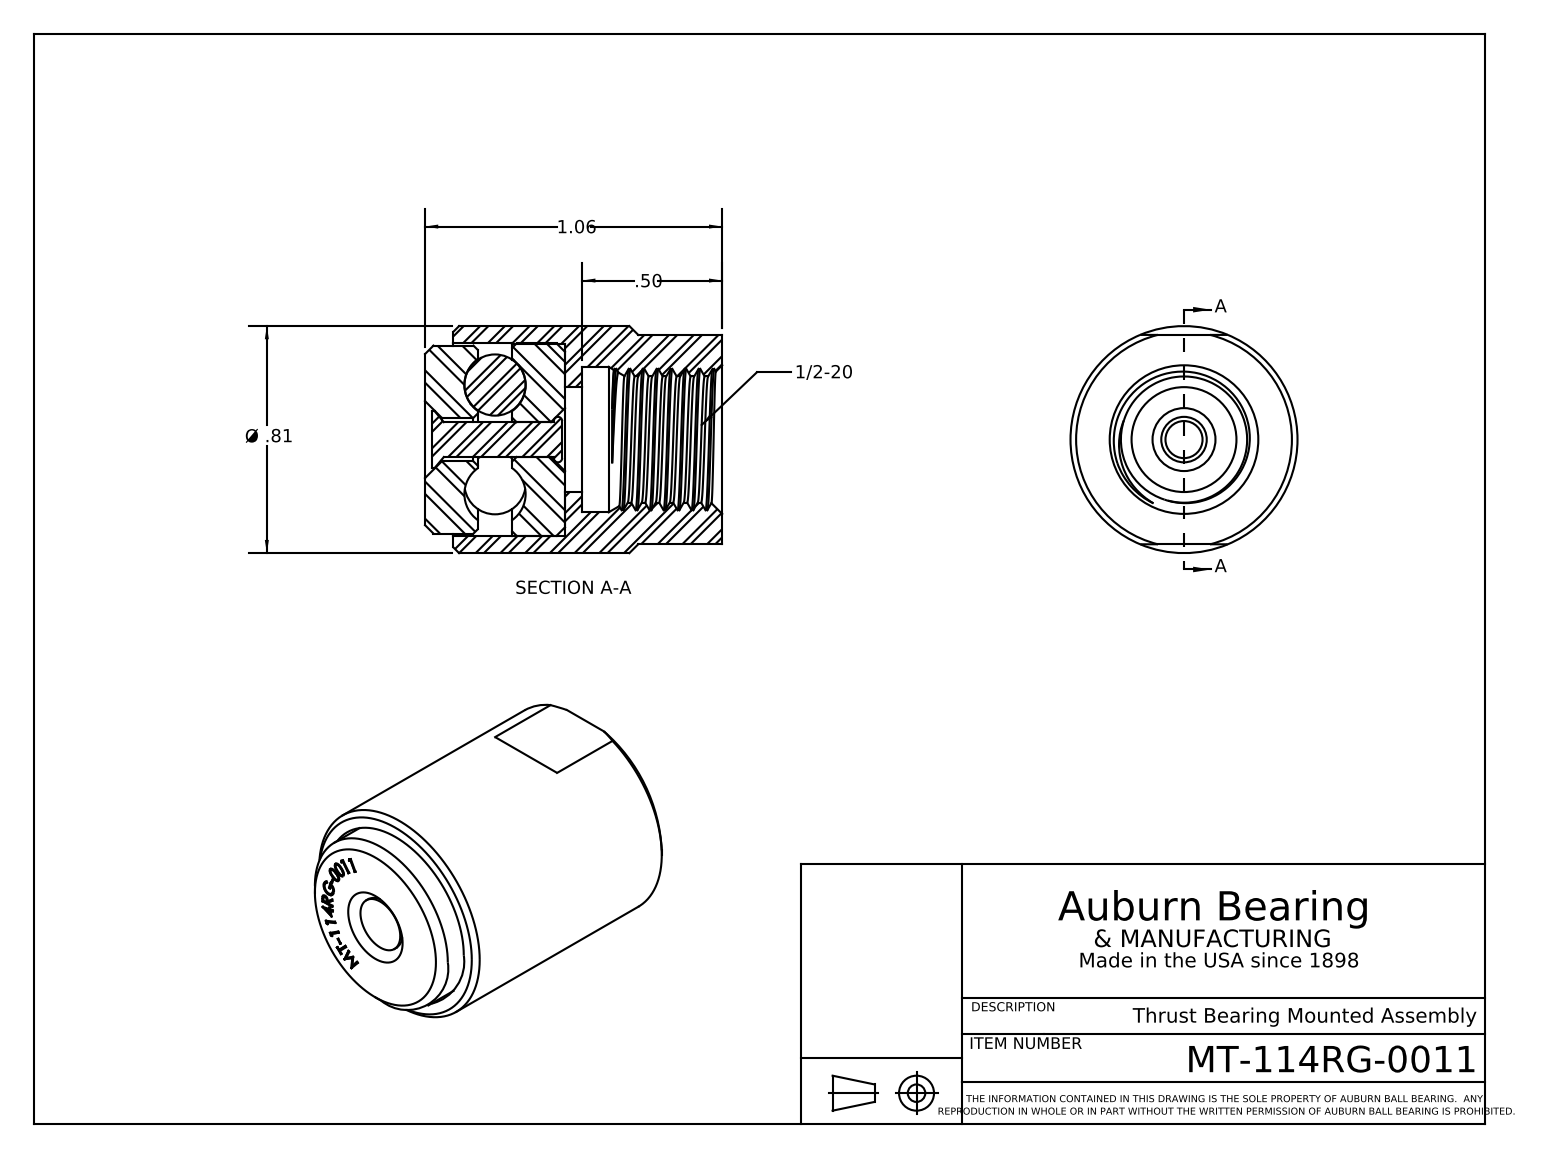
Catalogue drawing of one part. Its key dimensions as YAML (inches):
part_name: "MT-114RG-0011"
step_written_by: "SolidWorks 2020 (CONFIG_CONTROL_DESIGN)"
units: inches
bodies: {solids: 9, faces: 233, planar: 116, cylindrical: 36, other: 81}
overall_size: [1.062, 0.811, 0.811]
volume: 0.388
surface_area: 8.537
round_holes:
  - {diameter: 0.125, count: 1}
  - {diameter: 0.156, count: 1}
  - {diameter: 0.375, count: 1}
  - {diameter: 0.451, count: 1}
  - {diameter: 0.52, count: 1}
  - {diameter: 0.687, count: 1}
  - {diameter: 0.69, count: 1}
round_bosses_or_shafts:
  - {diameter: 0.811, count: 1}
  - {diameter: 0.687, count: 1}
  - {diameter: 0.672, count: 1}
  - {diameter: 0.201, count: 1}
face_to_face_distances: [0.562, 0.5, 1.062, 0.188, 0.312, 0.062, 0.25, 0.75, 0.102, 0.21]
